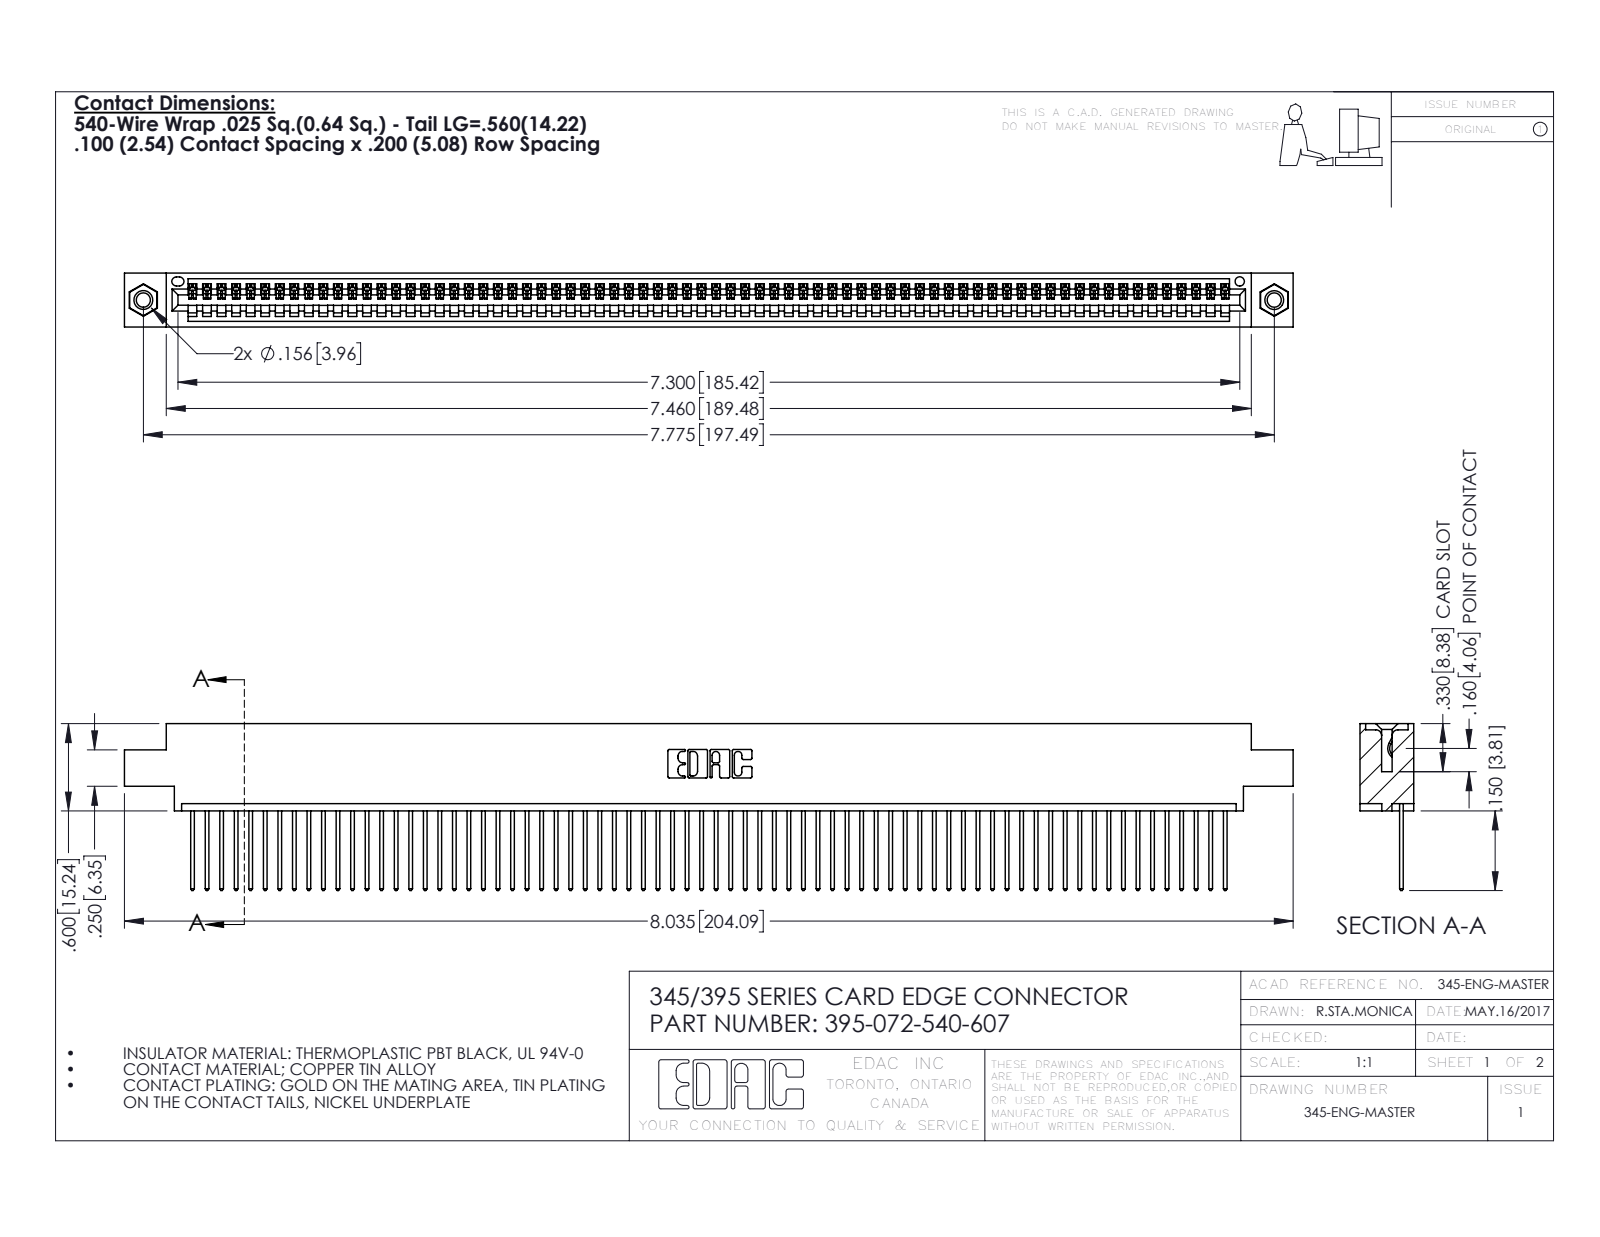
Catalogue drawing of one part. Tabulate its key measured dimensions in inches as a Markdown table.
| quantity | value |
| --- | --- |
| part name | 395-072-540-607; 345 Part_0.170 Offset - 0.156 Dia-TI; 345-250-001_345-250-005-103; 345-292-001_345-293-140 |
| STEP written by | SolidWorks 2016 (CONFIG_CONTROL_DESIGN) |
| units | inches |
| bodies | 75 solids, 4366 faces (2996 planar, 1354 cylindrical, 16 other) |
| overall size | 8.035 × 1.147 × 0.37 |
| volume | 1.196 in³ |
| surface area | 42.34 in² |
| round holes (diameter × count) | 0.098 × 2, 0.125 × 2, 0.156 × 2, 0.064 × 1 |
| round bosses / shafts (diameter × count) | 0.155 × 2 |
| partial cylindrical surfaces (radius × count) | 0.006 × 144, 0.01 × 144, 0.01 × 22, 0.007 × 6, 0.031 × 6, 0.026 × 3, 0.031 × 2, 0.04 × 2 |
| main face-to-face distances | 0.072, 0.298, 0.37, 0.098, 0.272, 0.025, 0.2, 0.225, 0.149, 0.175 |
| hole center spacings | 0.27, 7.539, 7.775 |
